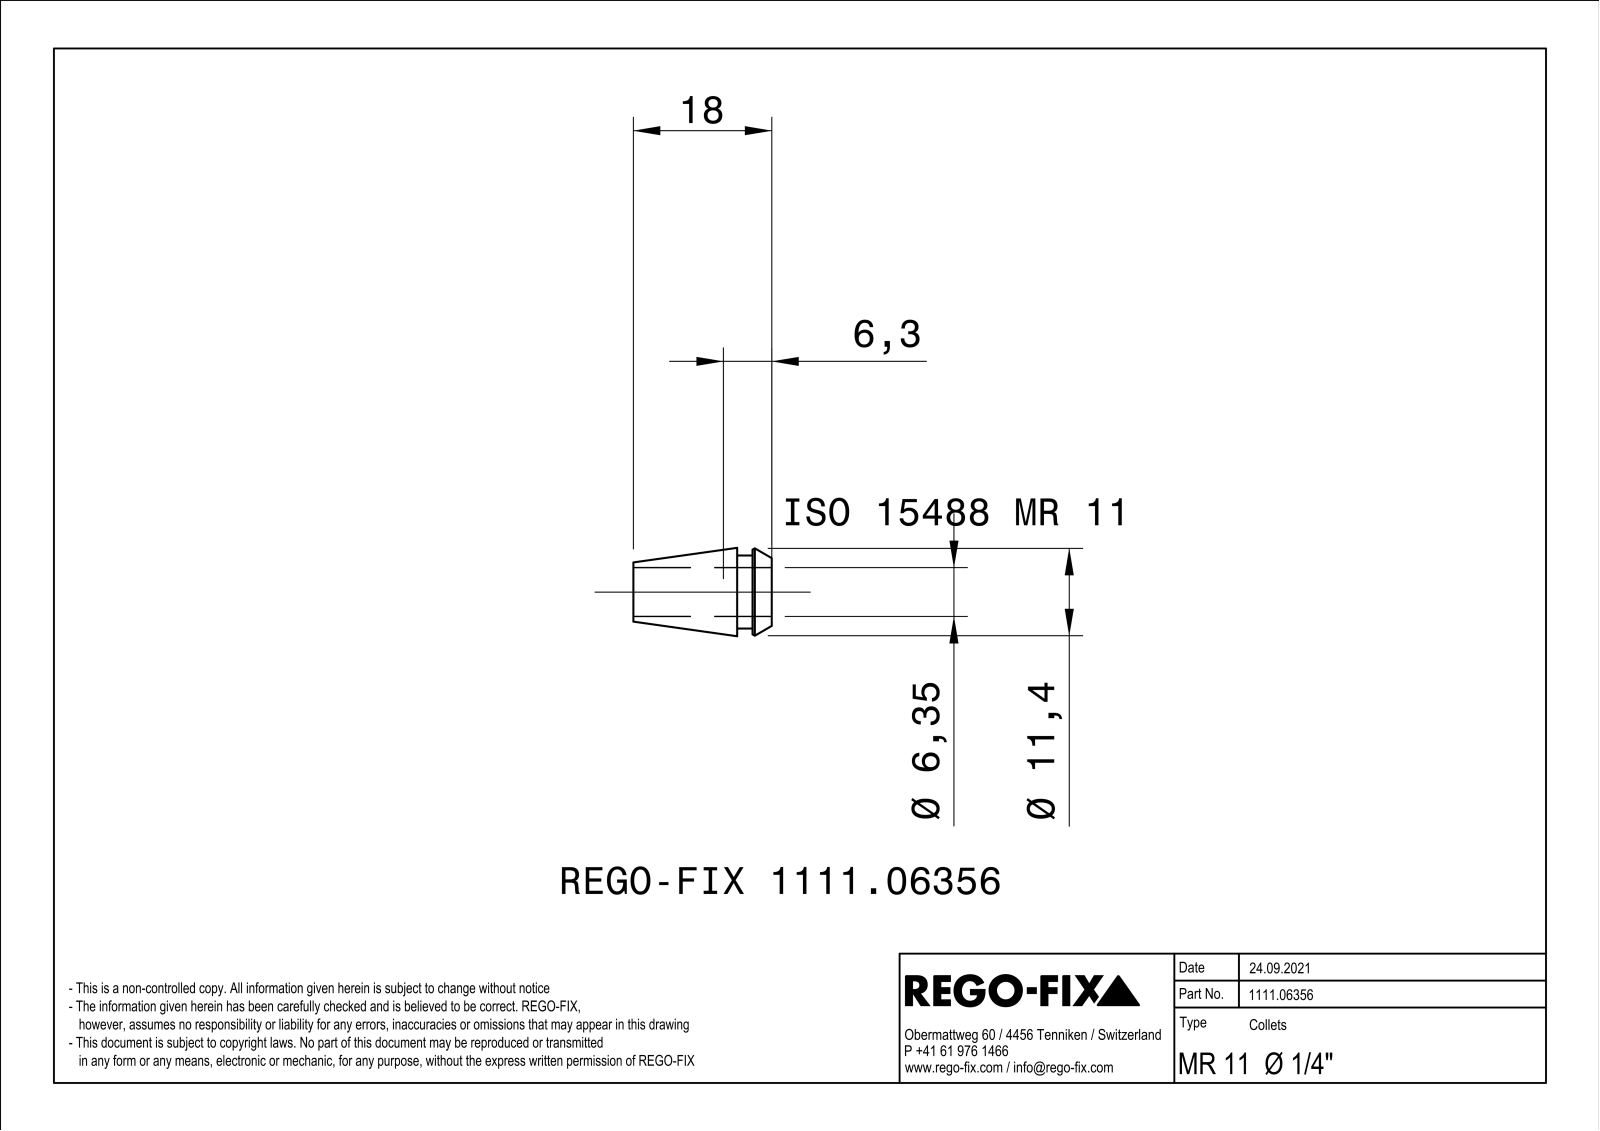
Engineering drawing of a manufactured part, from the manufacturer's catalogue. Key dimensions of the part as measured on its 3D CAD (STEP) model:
Part name (STEP PRODUCT): NOCUT
STEP written by: SIEMENS PLM Software Solid Edge ST10 (AUTOMOTIVE_DESIGN)
Units: millimetres
Bodies: 1 solid, 193 faces (60 planar, 37 cylindrical, 96 other)
Overall size (bounding box): 18 × 11.43 × 11.43
Volume: 610 mm³ · Surface area: 1 506 mm²
Round holes (diameter × count): ⌀6.35 ×1
Round bosses / shafts (diameter × count): ⌀11.44 ×1, ⌀9.5 ×1
Partial cylindrical surfaces — rounded edges, fillets, slot ends (radius × count): R0.23 ×12
Main face-to-face distances: 0.45, 0.46, 0.44, 2, 2.5, 4.5, 18, 15.5, 13.5
